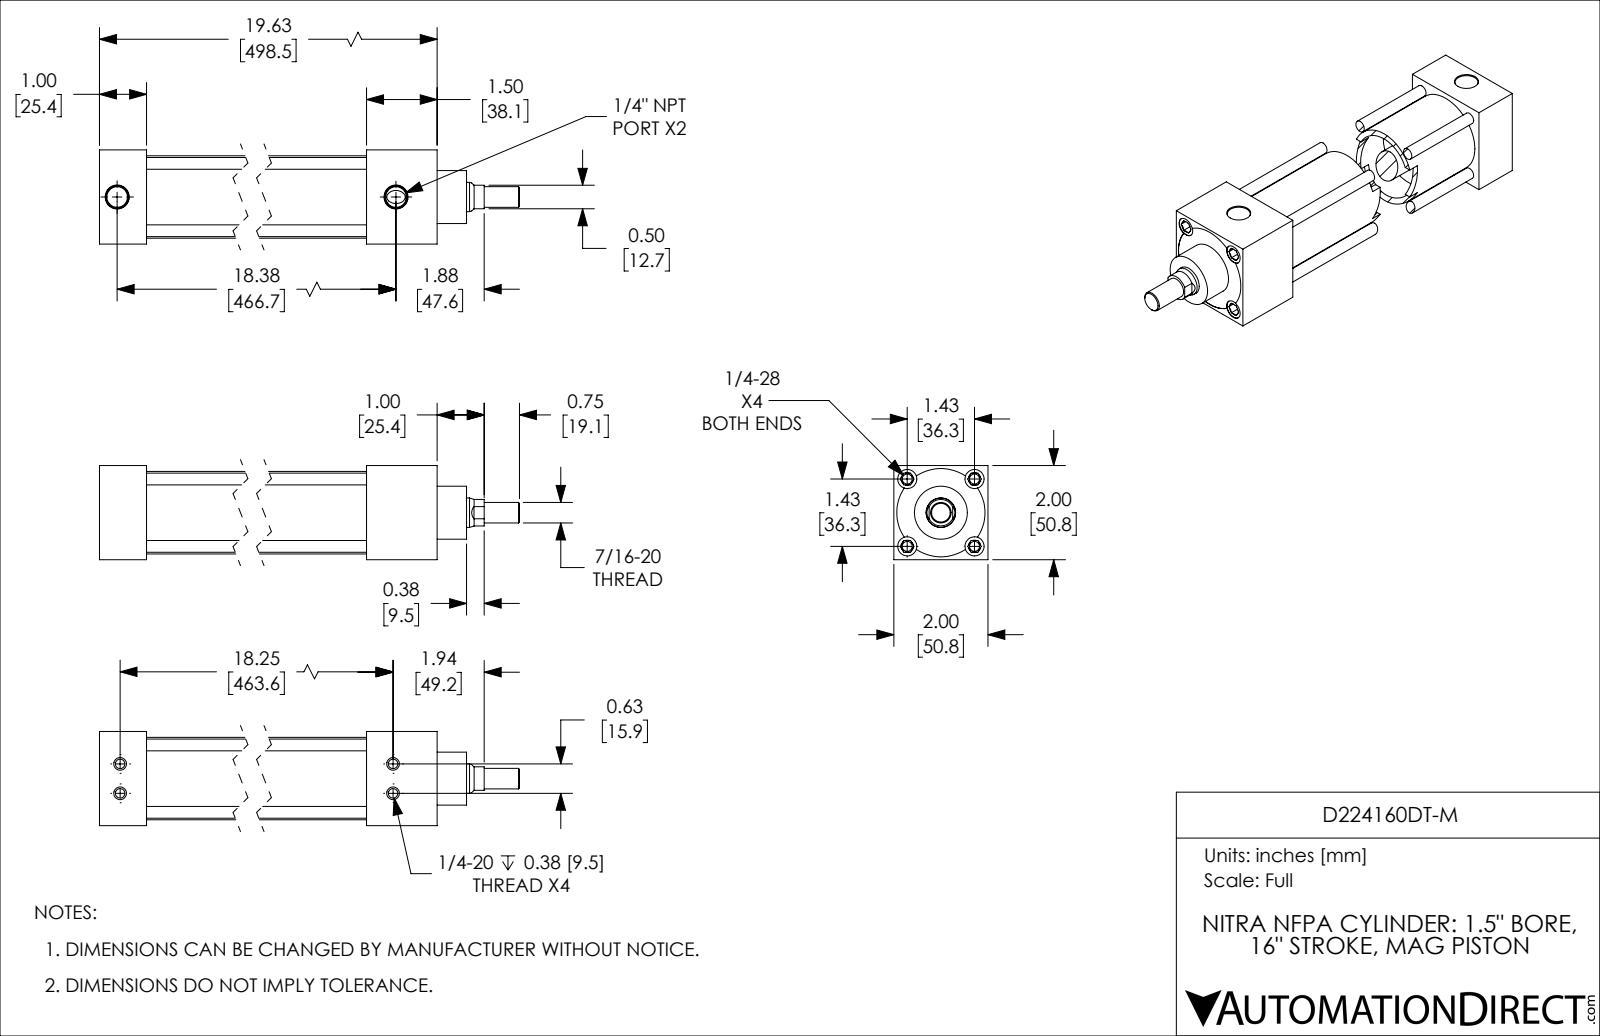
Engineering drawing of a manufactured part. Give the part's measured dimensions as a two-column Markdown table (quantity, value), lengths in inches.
| quantity | value |
| --- | --- |
| part name | D224160DT-M_BODY; D224160DT-M_PISTON_KK1; D224160DT-M |
| STEP written by | SolidWorks 2019 (CONFIG_CONTROL_DESIGN) |
| units | inches |
| bodies | 2 solids, 203 faces (58 planar, 65 cylindrical, 80 other) |
| overall size | 21.375 × 2 × 2 |
| volume | 31.43 in³ |
| surface area | 322.4 in² |
| round holes (diameter × count) | 0.201 × 4, 0.213 × 4, 0.406 × 4, 0.438 × 2, 0.626 × 1, 1.501 × 1 |
| round bosses / shafts (diameter × count) | 0.25 × 4, 1.751 × 1, 1.499 × 1, 1.125 × 1, 0.624 × 1, 0.437 × 1 |
| partial cylindrical surfaces (radius × count) | 0.281 × 1, 0.937 × 1 |
| main face-to-face distances | 2, 1, 18.125, 17.125, 2.125, 19.62, 18.62, 1.495, 1.125, 16 |
| hole center spacings | 0.319, 1.011, 1.43, 0.625, 2.022, 18.25, 18.261, 18.315 |
